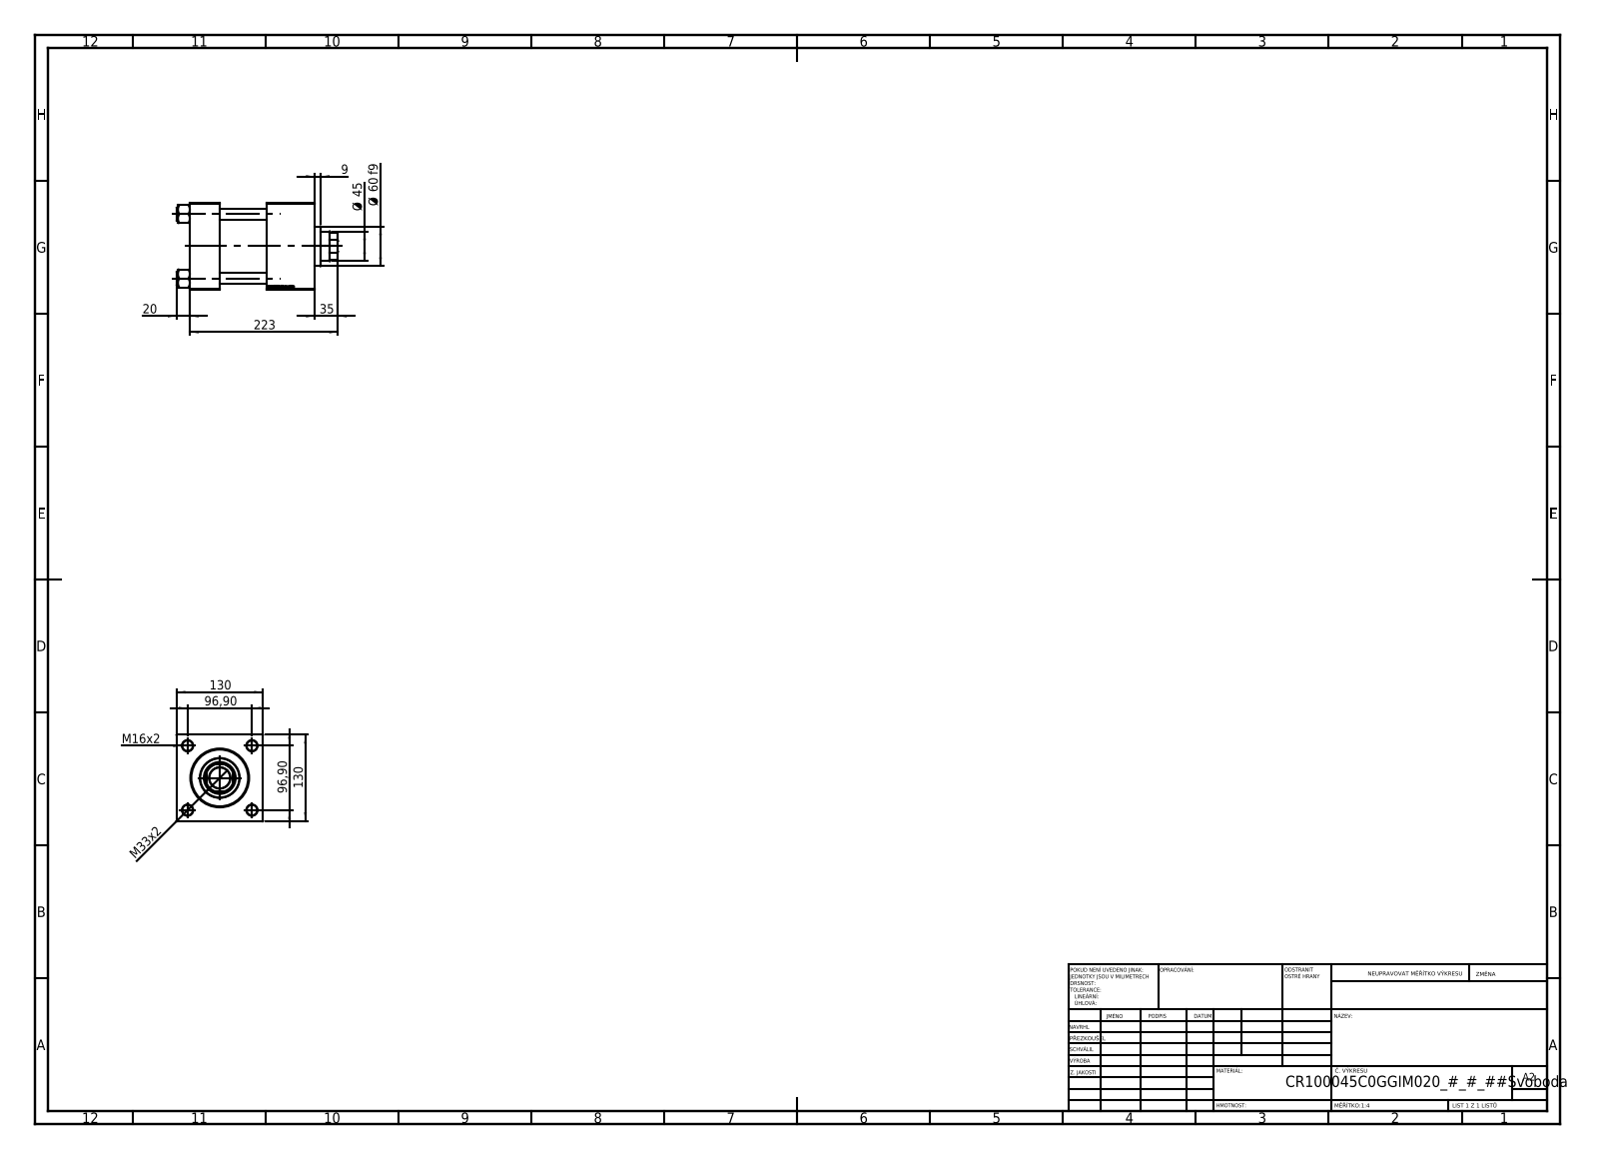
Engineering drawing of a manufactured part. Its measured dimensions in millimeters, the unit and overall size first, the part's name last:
Units: millimetres
Overall size (bounding box): 243 × 130 × 130
Round holes (diameter × count): ⌀16 ×4, ⌀7 ×2, ⌀26.44 ×2, ⌀35 ×2, ⌀31.5 ×1, ⌀45 ×1, ⌀48 ×1, ⌀76 ×1, ⌀85.5 ×1, ⌀100 ×1
Round bosses / shafts (diameter × count): ⌀19 ×4, ⌀106 ×1, ⌀60 ×1
Partial cylindrical surfaces — rounded edges, fillets, slot ends (radius × count): R22 ×1
Main face-to-face distances: 130, 45, 188, 143, 116, 71, 72, 20, 96, 51
Hole centre spacings: 68.52, 96.9, 137.04, 118.5
Volume: 2 425 000 mm³ · Surface area: 326 396 mm²
Bodies: 11 solids, 1197 faces (574 planar, 87 cylindrical, 536 other)
Part name (STEP PRODUCT): NUT_M5_C; V215CR_VCP_C; V215_VC_A; V215CR_C_TYCINKA (+1 more)
STEP written by: SolidWorks 2019 (CONFIG_CONTROL_DESIGN)
